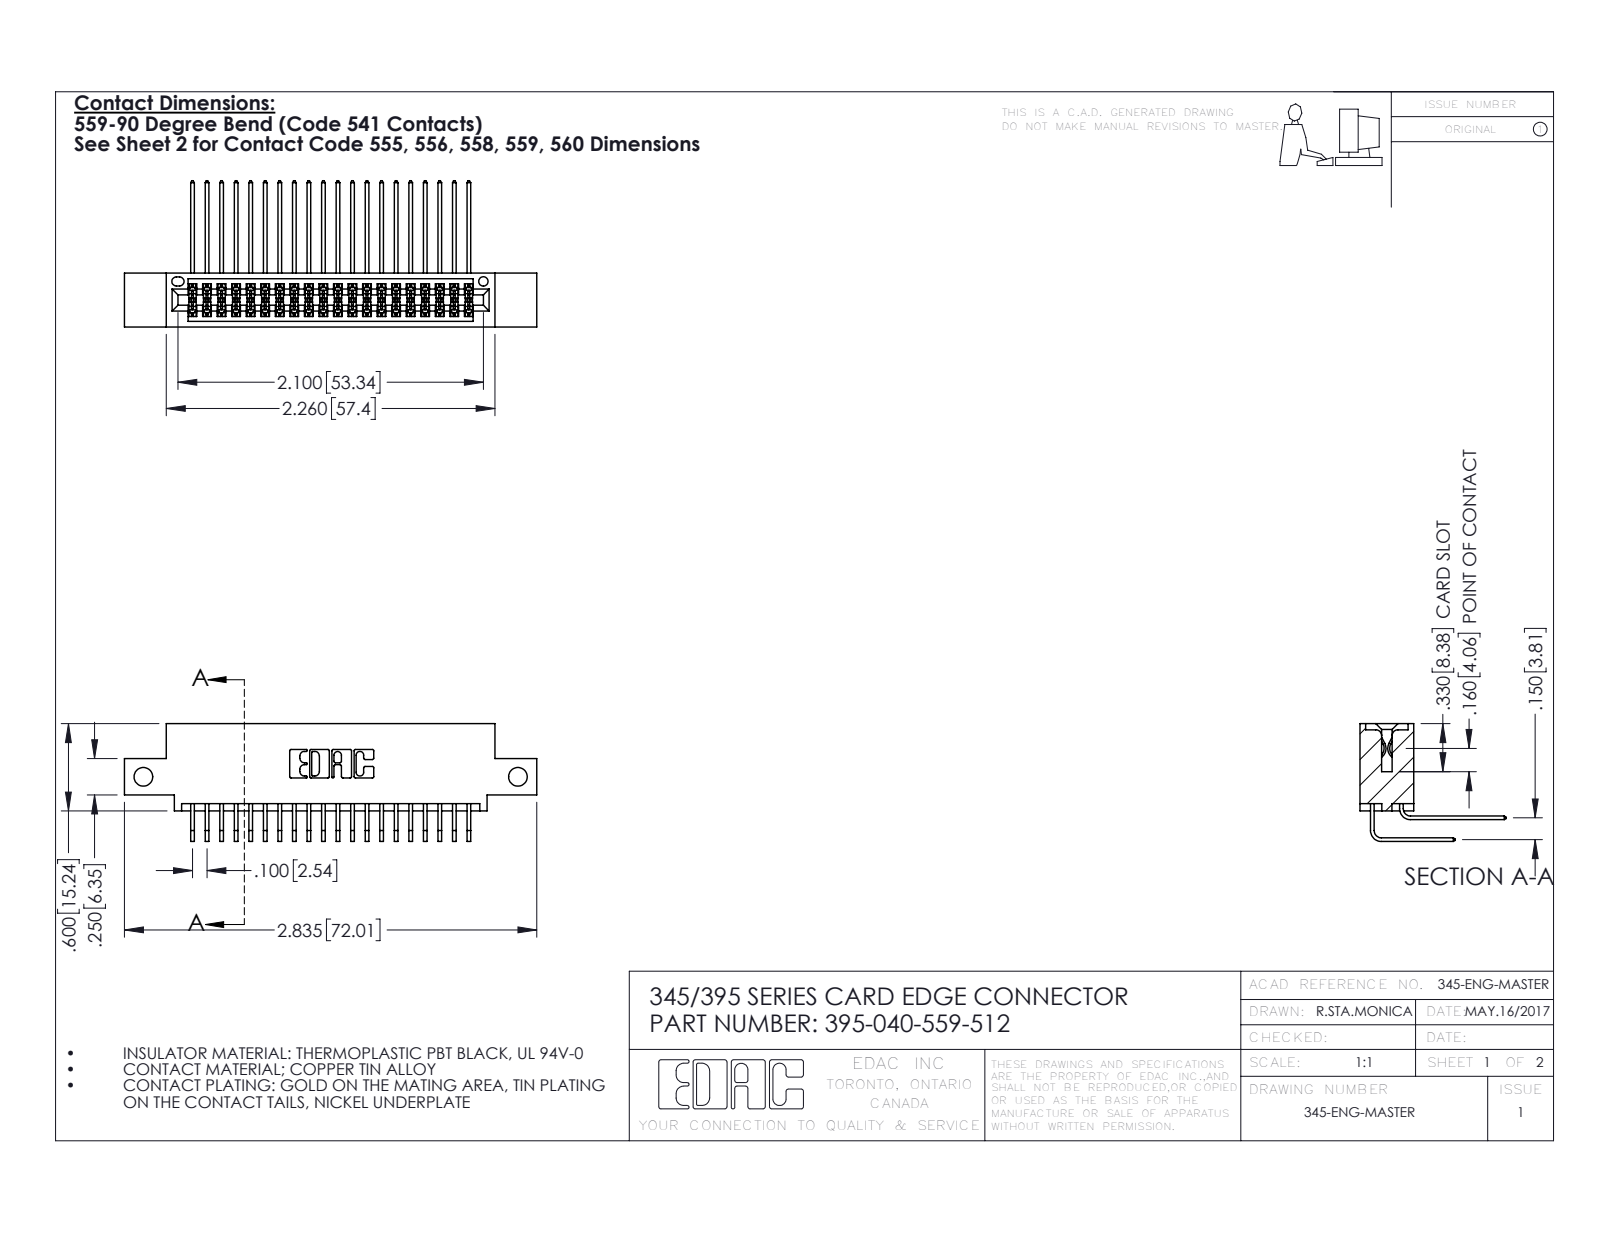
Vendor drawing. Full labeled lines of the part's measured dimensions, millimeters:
Part name (STEP PRODUCT): 345-292-001_559 Tail - 2; 395-040-559-512; 345-292-001_558 559 Tail - 1; 345 Part_0.110 Offset - Side Mount
STEP written by: SolidWorks 2016 (CONFIG_CONTROL_DESIGN)
Units: millimetres
Bodies: 41 solids, 2210 faces (1484 planar, 726 cylindrical, 0 other)
Overall size (bounding box): 72 × 25.5 × 20.5
Volume: 6 870 mm³ · Surface area: 10 750 mm²
Round holes (diameter × count): ⌀3.3 ×2, ⌀1.6 ×1
Partial cylindrical surfaces — rounded edges, fillets, slot ends (radius × count): R0.2 ×61, R0.3 ×22, R0.2 ×6, R0.8 ×6, R0.7 ×3, R0.4 ×2, R0.5 ×2, R0.6 ×2
Main face-to-face distances: 1.8, 7.6, 5.1, 9.4, 2.5, 6.9, 0.6, 5.7, 3.8, 4.4
Hole centre spacings: 65.4
